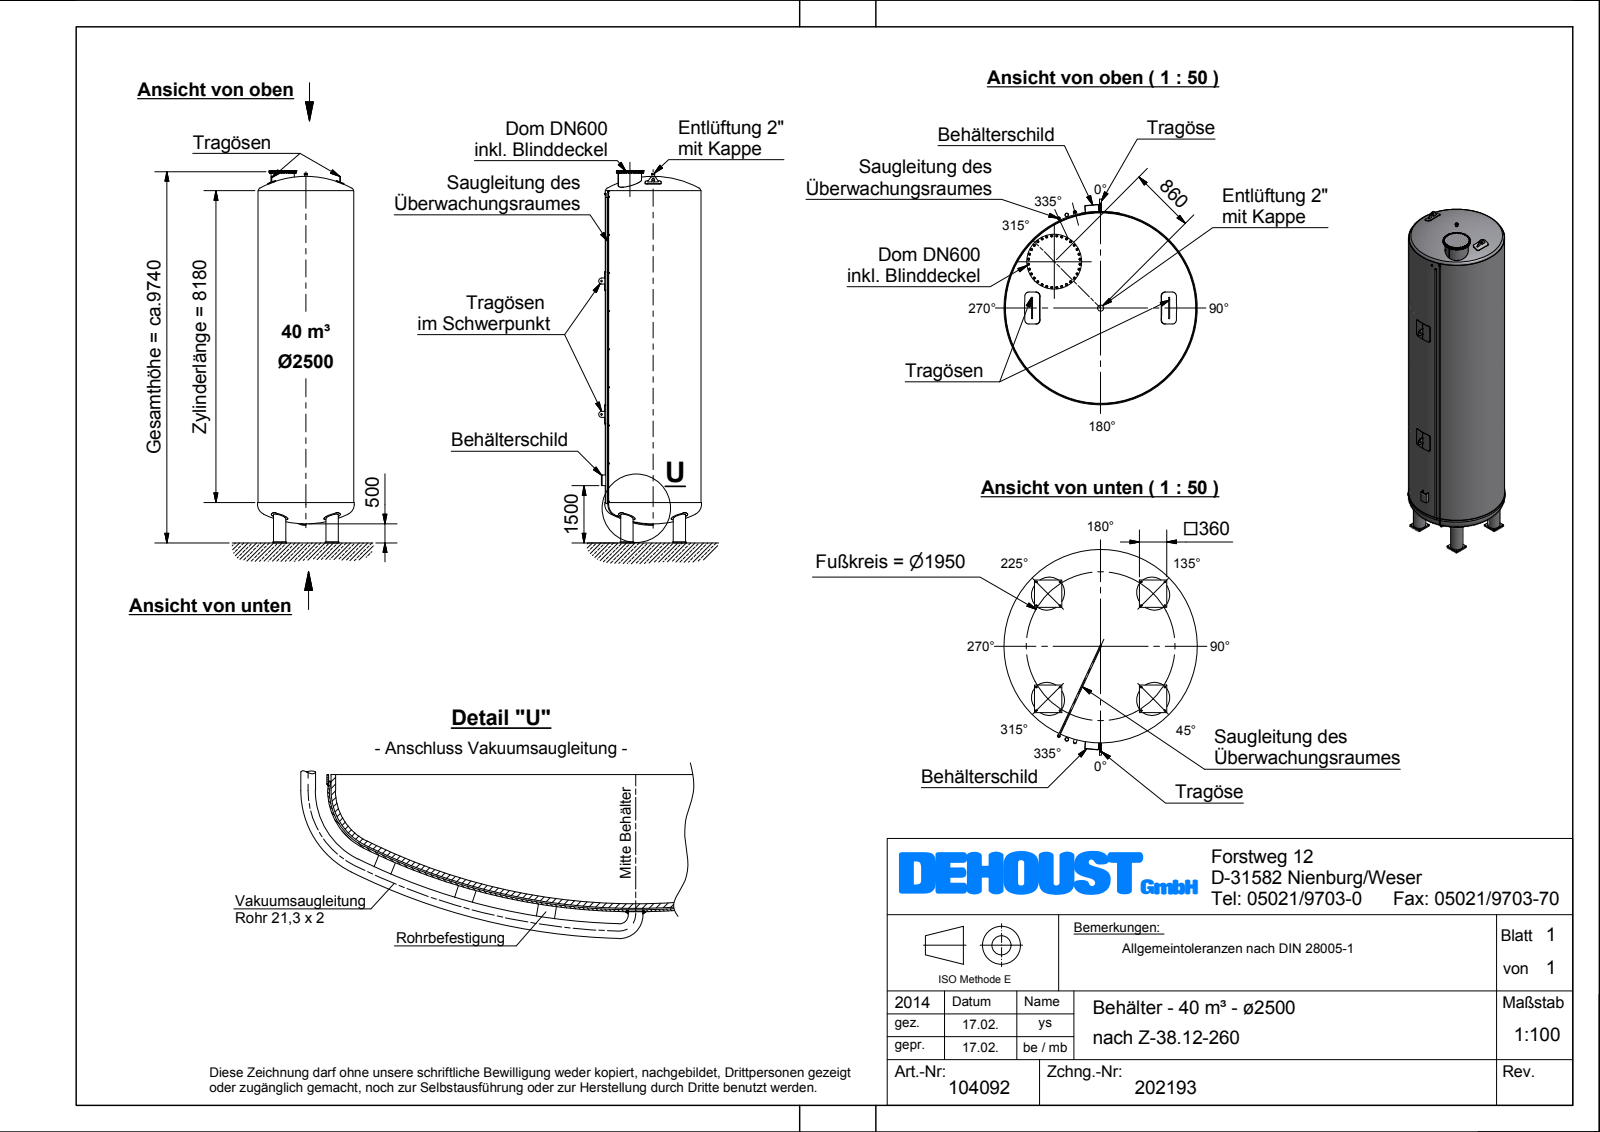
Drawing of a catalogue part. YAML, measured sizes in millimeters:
part_name: "Z-38_12-260_Beh\\S\\dlter_\\S\\x2500_040m\\S\\3_Dichte=1,0"
step_written_by: "Autodesk Inventor 2012 (AUTOMOTIVE_DESIGN)"
units: millimeters
bodies: {solids: 17, faces: 1242, planar: 744, cylindrical: 164, other: 334}
overall_size: [9768.78, 2700, 2540]
volume: 42760000000
surface_area: 99730000
round_holes:
  - {diameter: 200, count: 4}
  - {diameter: 306.9, count: 4}
  - {diameter: 598, count: 1}
round_bosses_or_shafts:
  - {diameter: 22.5, count: 32}
  - {diameter: 16, count: 32}
  - {diameter: 450, count: 4}
  - {diameter: 323.9, count: 4}
  - {diameter: 21.3, count: 2}
  - {diameter: 2540, count: 1}
  - {diameter: 2516, count: 1}
  - {diameter: 720, count: 1}
partial_cylinders:
  - {radius: 50, count: 8}
  - {radius: 56, count: 8}
  - {radius: 80, count: 2}
  - {radius: 35, count: 1}
  - {radius: 85, count: 1}
  - {radius: 1259, count: 1}
  - {radius: 1269, count: 1}
face_to_face_distances: [9241.09, 30, 9211.09, 9758.78, 9728.78, 517.69, 9723.78, 9693.78, 482.69, 35]
hole_center_spacings: [1378.86, 1300.09, 1950, 115, 1835]
